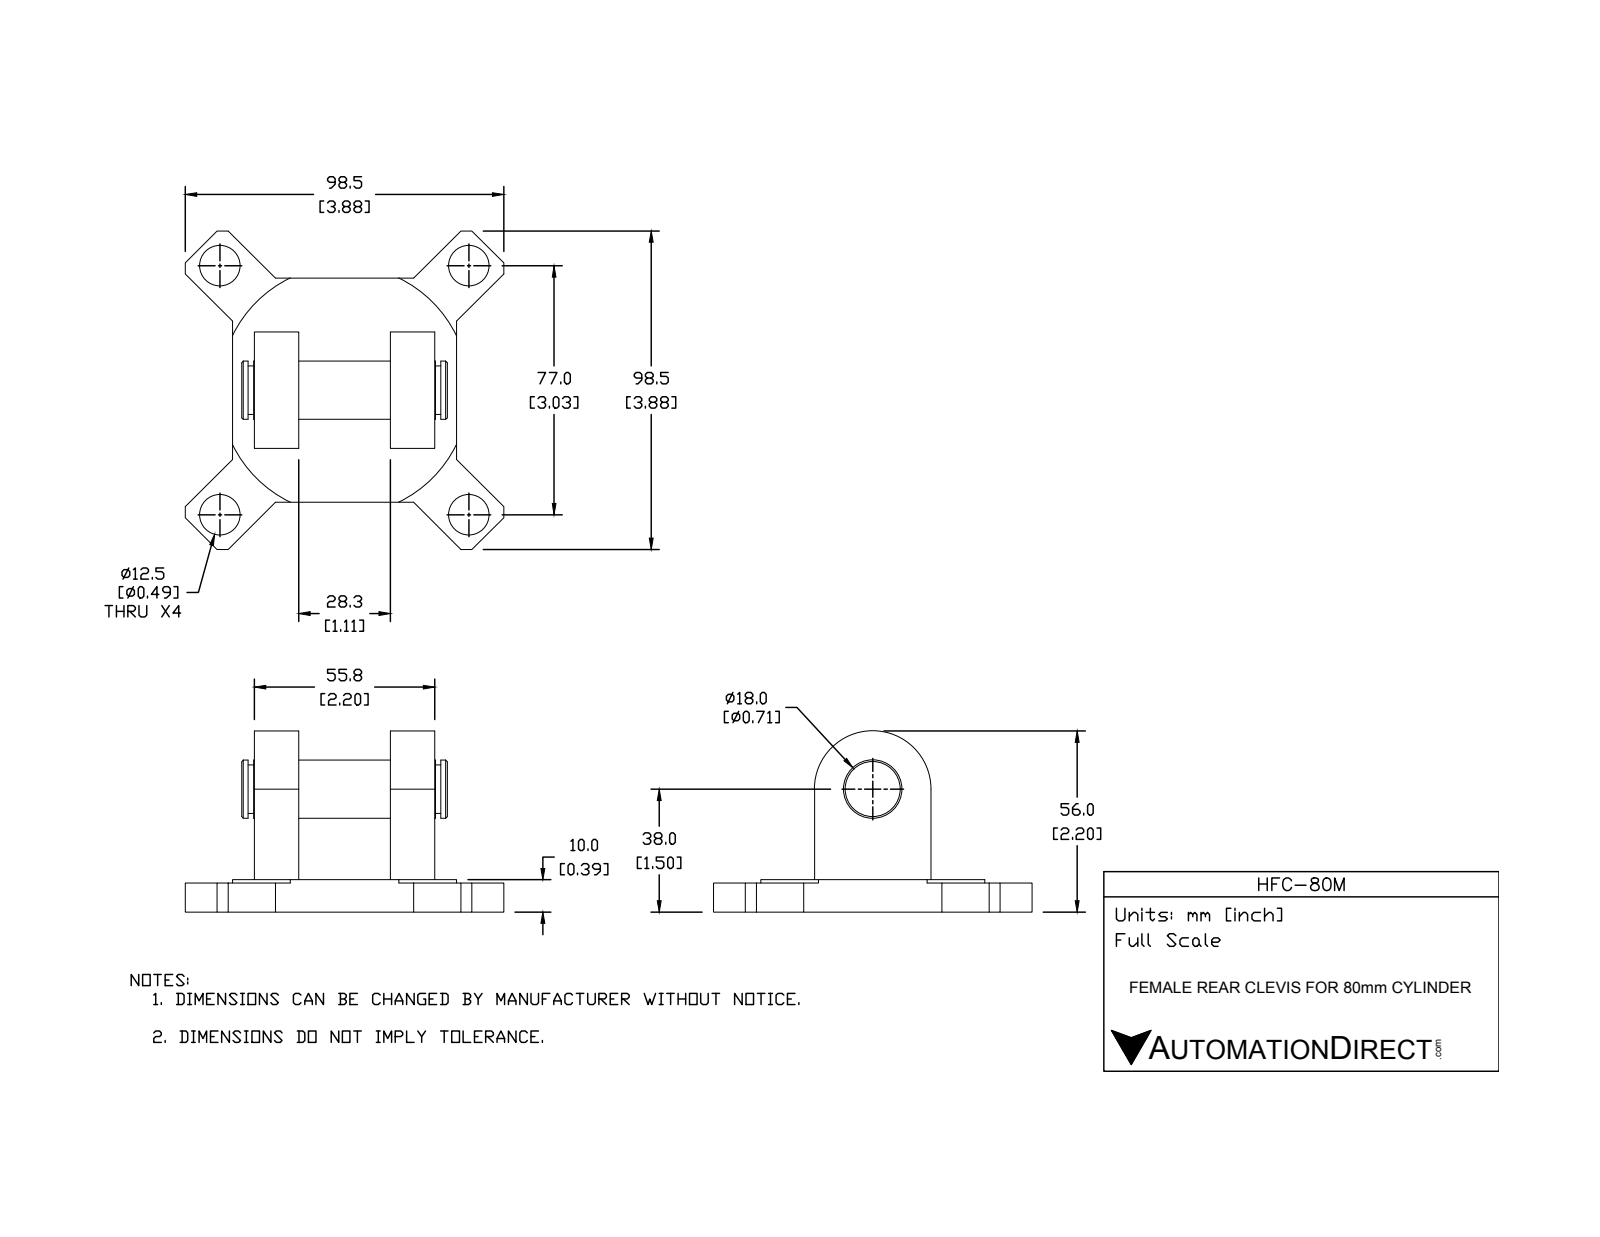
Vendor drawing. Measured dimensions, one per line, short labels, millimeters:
name: HFC-80M
written by: SolidWorks 2015 (CONFIG_CONTROL_DESIGN)
unit: mm
bodies: 2 solids, 76 faces (44 planar, 28 cylindrical, 4 other)
size: 98.5 × 98.5 × 56
volume: 105 929 mm³; area: 29 818 mm²
holes: 4× ⌀12.5
bosses: 1× ⌀18, 1× ⌀15
rounds: 1× R18, 1× R38.5
face distances: 10, 13.75, 42.05, 9, 1, 55.8, 28.3, 6.75, 20.5, 48.8
hole spacings: 77, 108.89
